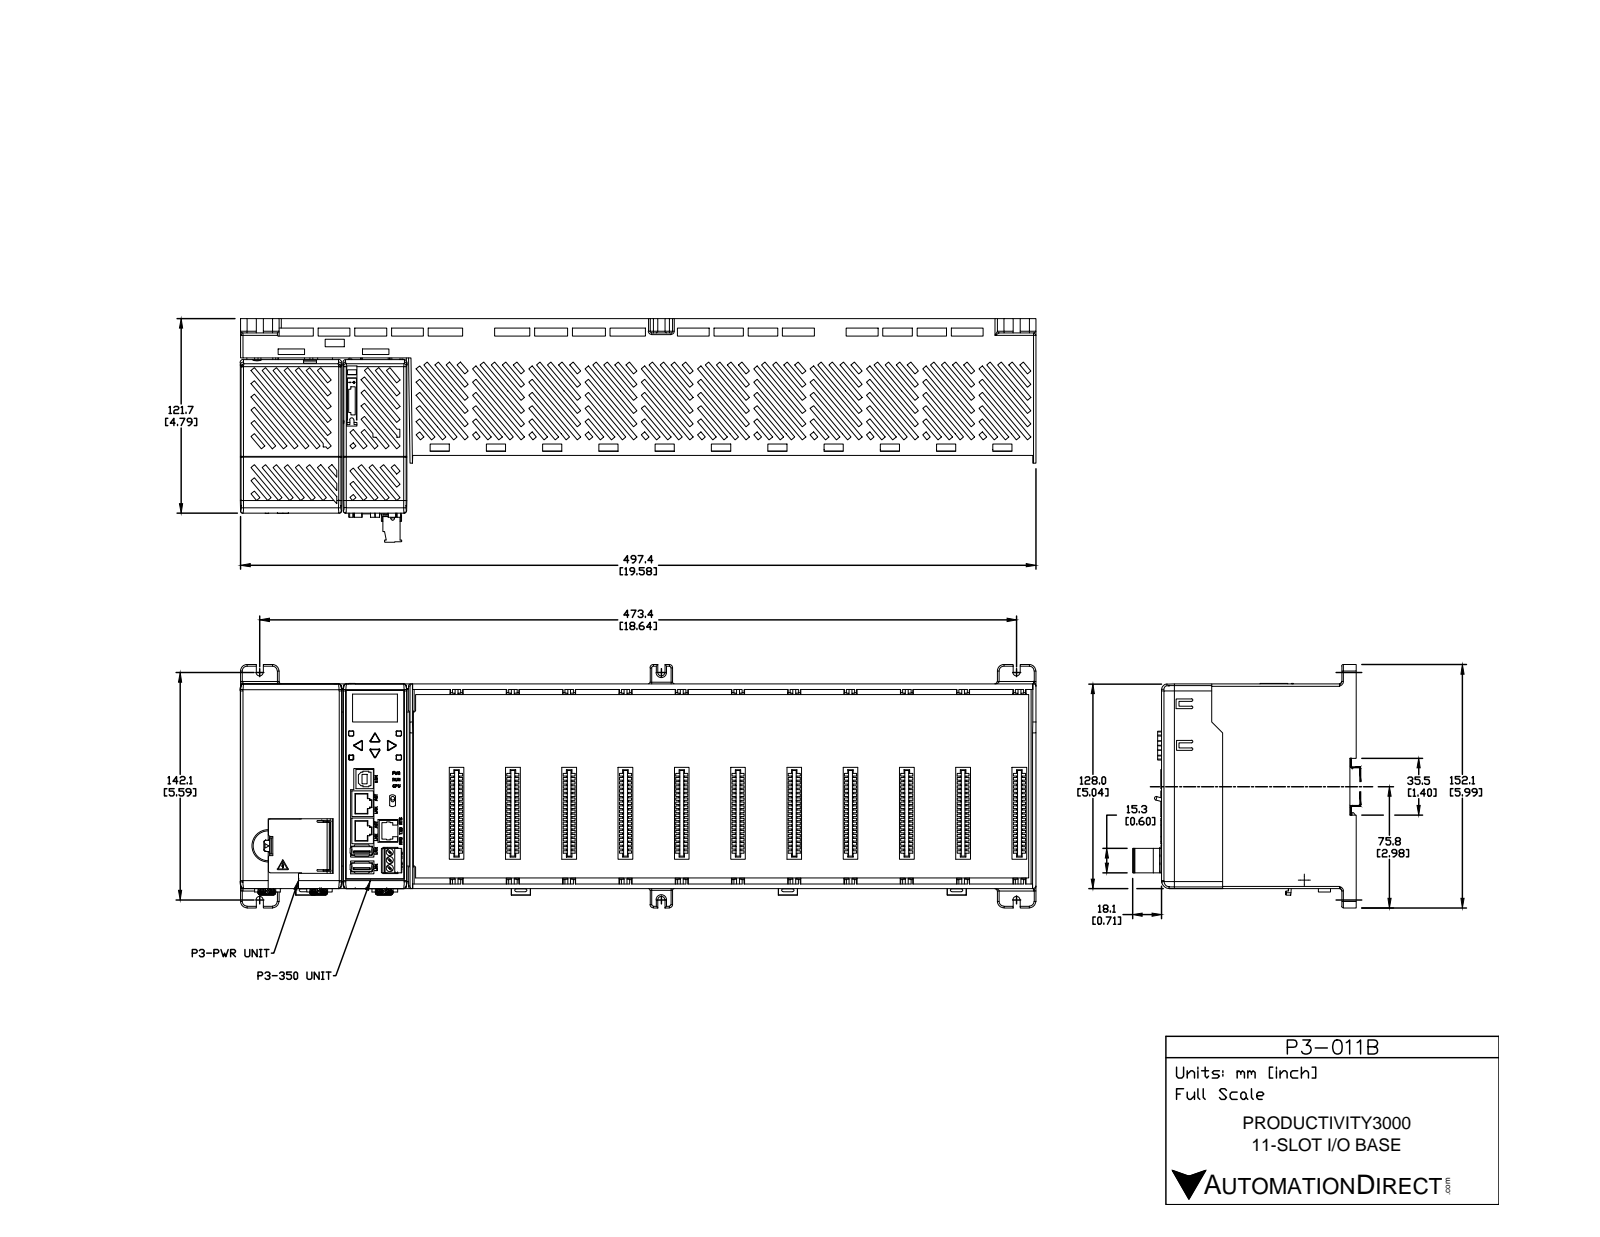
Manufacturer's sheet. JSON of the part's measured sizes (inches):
{"part_name": "P3-11B", "step_written_by": "SolidWorks 2009 (CONFIG_CONTROL_DESIGN)", "units": "inches", "bodies": {"solids": 1, "faces": 622, "planar": 610, "cylindrical": 12, "other": 0}, "overall_size": [19.58, 5.98, 3.5], "volume_in3": 40.35, "surface_area_in2": 751.6, "partial_cylinders_radius": [[0.16, 8], [0.09, 4]], "face_to_face_distances": [0.075, 0.429, 0.12, 0.624, 0.549, 0.504, 0.075, 5.04, 4.965, 4.89]}
